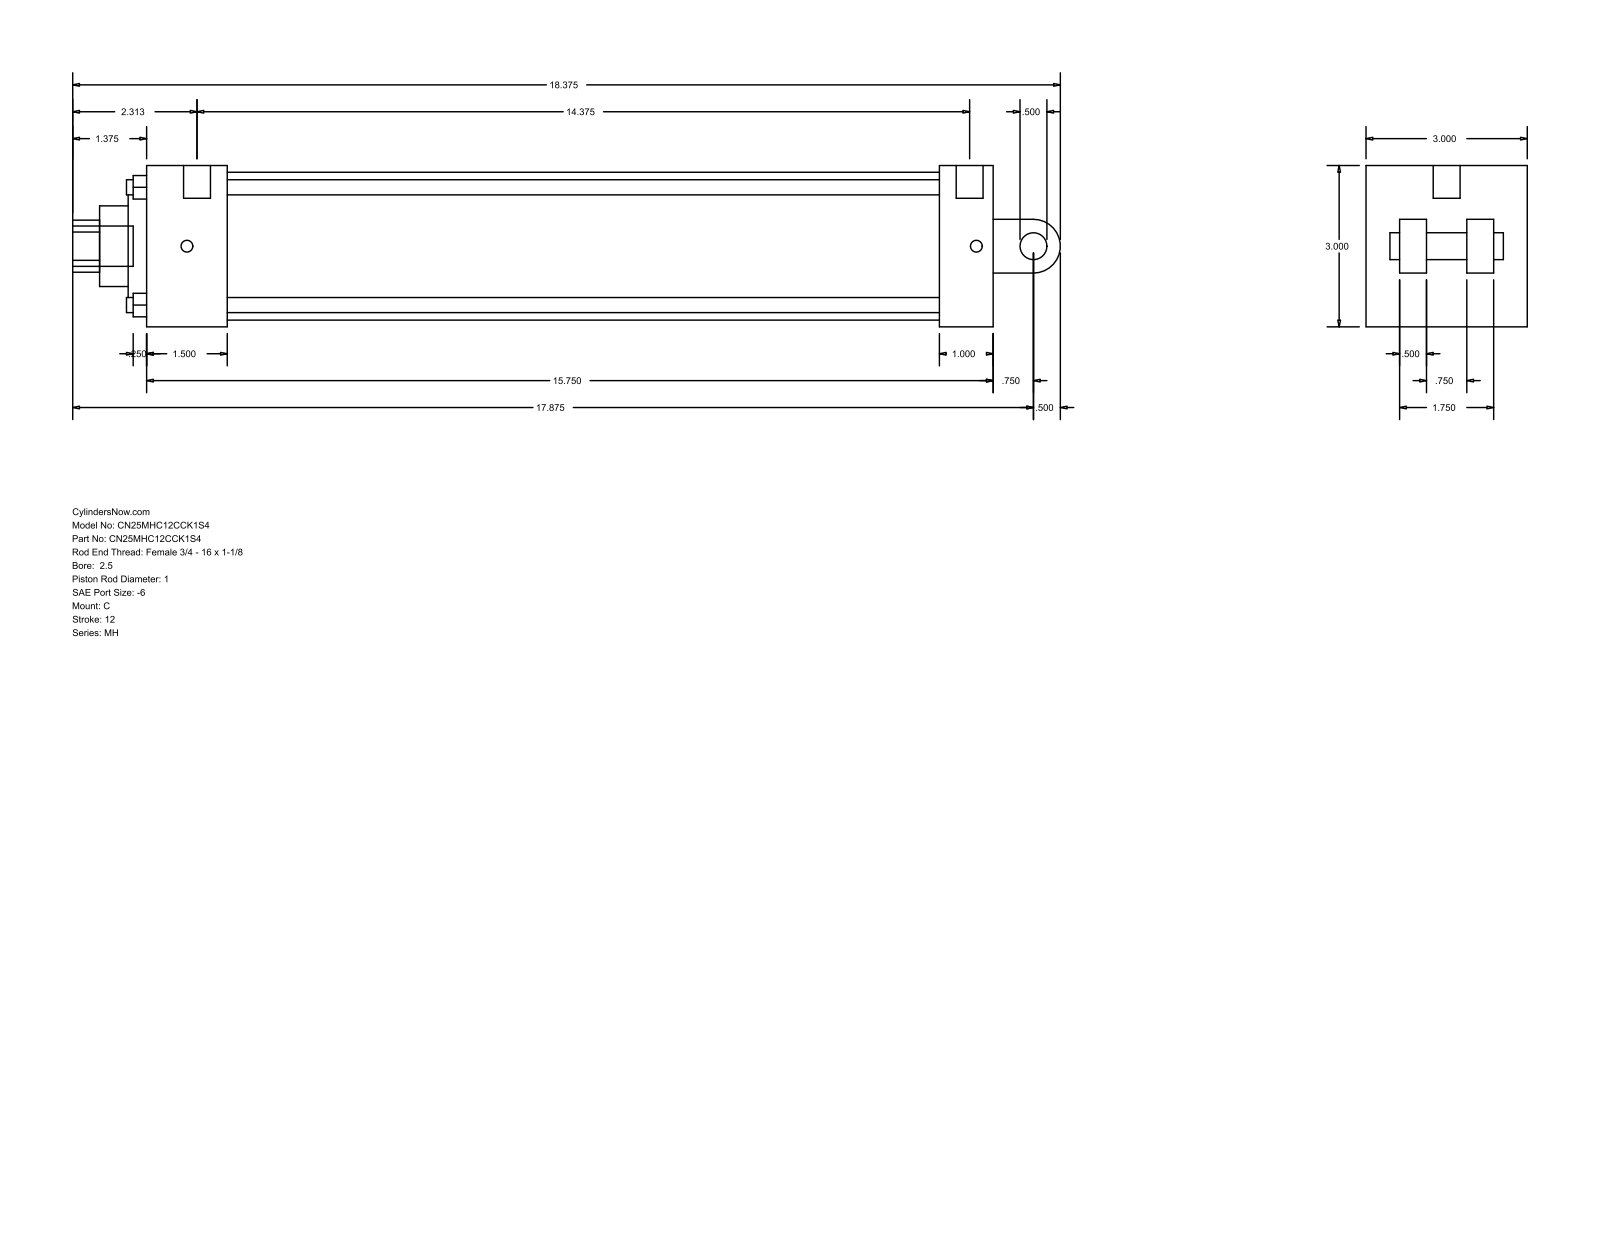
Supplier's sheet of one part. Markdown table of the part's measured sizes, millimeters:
| quantity | value |
| --- | --- |
| part name | MH_C__0250_1 |
| STEP written by | GSSL Pune (CONFIG_CONTROL_DESIGN) |
| units | millimeters |
| bodies | 0 solids, 101 faces (71 planar, 30 cylindrical, 0 other) |
| overall size | 466.73 × 76.2 × 76.2 |
| round holes (diameter × count) | 7.14 × 4, 5.56 × 2, 12.7 × 1, 25.4 × 1, 38.1 × 1, 60.33 × 1, 69.85 × 1 |
| round bosses / shafts (diameter × count) | 12.7 × 2, 5.56 × 2, 19.05 × 1 |
| partial cylindrical surfaces (radius × count) | 12.29 × 1, 12.7 × 1 |
| main face-to-face distances | 76.2, 400.06, 15.87, 60.33, 374.65, 25.41, 38.11, 336.54, 361.95, 12.7 |
| hole center spacings | 39.33, 55.62, 78.66, 3.18 |
